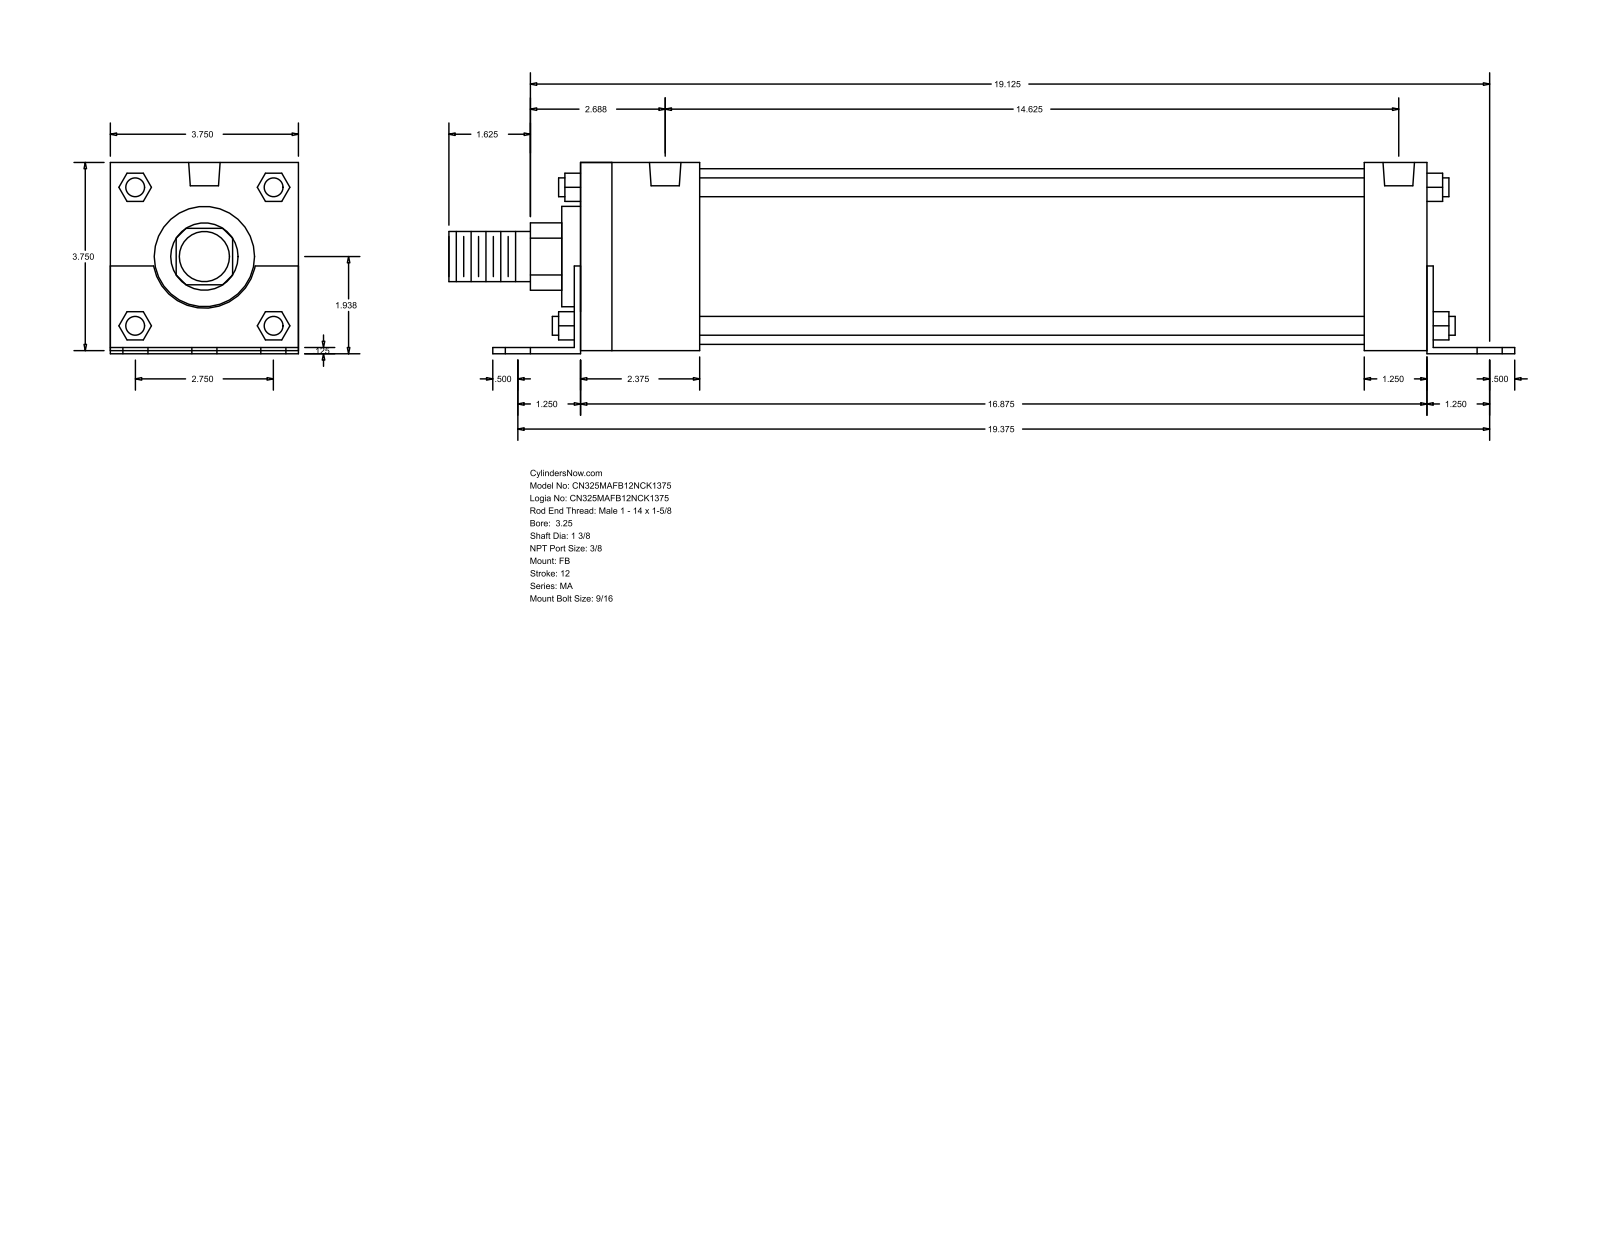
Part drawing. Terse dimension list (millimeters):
name: MA_FB__0325_1.375
written by: GSSL Pune (CONFIG_CONTROL_DESIGN)
unit: mm
bodies: 0 solids, 140 faces (105 planar, 35 cylindrical, 0 other)
size: 539.75 × 96.84 × 95.25
holes: 6× ⌀14.29, 4× ⌀11.11, 2× ⌀15.93
bosses: 4× ⌀9.53, 1× ⌀88.9, 1× ⌀50.8, 1× ⌀34.92, 1× ⌀25.4
rounds: 1× R17.06, 1× R26.16
face distances: 95.24, 3.17, 1.59, 96.83, 1.58, 93.66, 3.18, 428.62, 431.8, 31.75
hole spacings: 34.92, 493.36, 492.12, 57.78, 61.64, 69.84, 82.38, 86.72
